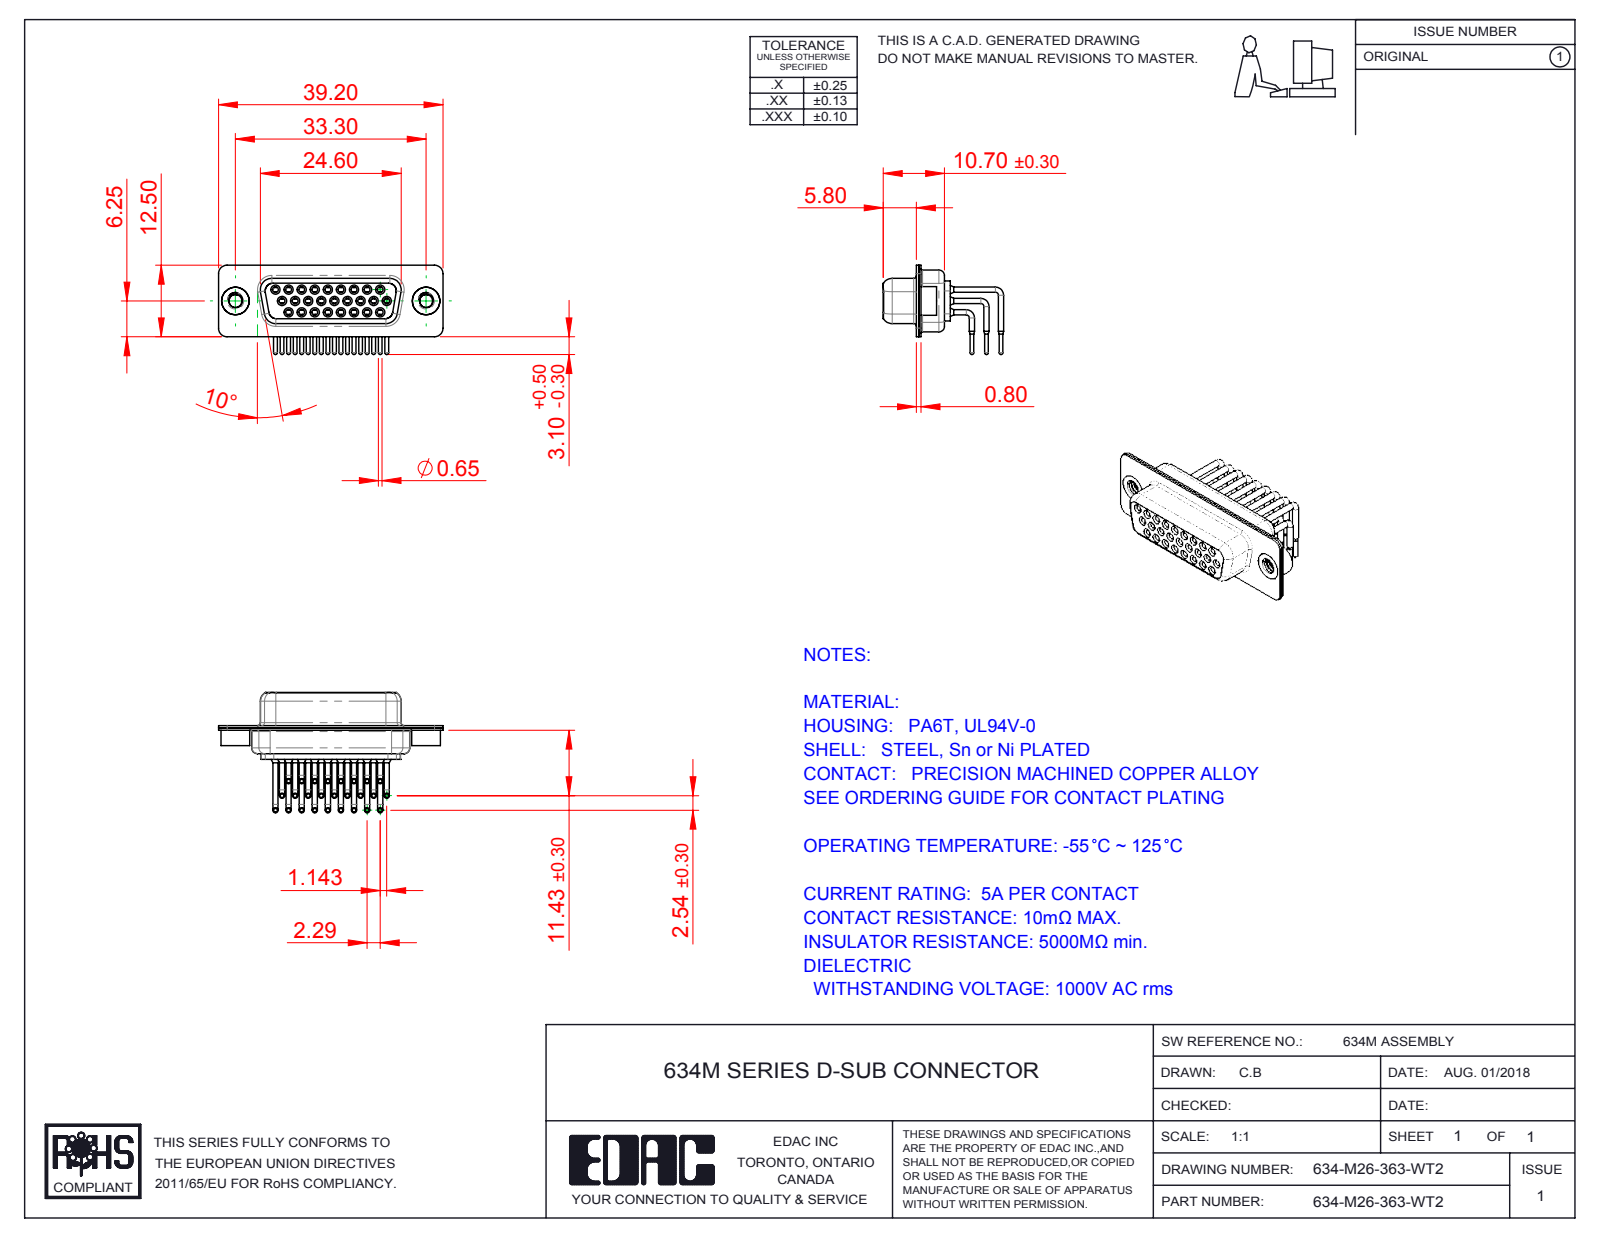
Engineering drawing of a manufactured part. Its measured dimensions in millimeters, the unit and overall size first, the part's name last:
Units: millimetres
Overall size (bounding box): 39.2 × 21.02 × 15.6
Round holes (diameter × count): ⌀1 ×26, ⌀1.1 ×26, ⌀1.7 ×26, ⌀1.8 ×26, ⌀2 ×26, ⌀2.26 ×2, ⌀4 ×2, ⌀4.8 ×2
Round bosses / shafts (diameter × count): ⌀0.9 ×52, ⌀1.6 ×26, ⌀1.5 ×26, ⌀0.65 ×26, ⌀5 ×2, ⌀4.9 ×2, ⌀2 ×1
Partial cylindrical surfaces — rounded edges, fillets, slot ends (radius × count): R1.5 ×16, R2 ×12, R1.35 ×8, R1.6 ×8, R0.25 ×4, R0.5 ×4, R0.6 ×4, R0.65 ×4
Main face-to-face distances: 0.4, 2.3, 1.45, 8.95, 8.5, 1.9, 0.8, 6.2, 0.45, 7.05
Hole centre spacings: 3.96, 2.28, 4.57, 6.05, 2.29, 8.24, 6.86, 6.04
Volume: 2 533 mm³ · Surface area: 8 471 mm²
Bodies: 31 solids, 1657 faces (457 planar, 735 cylindrical, 465 other)
Part name (STEP PRODUCT): 634M Contact Row 2; 634M Shell Front_26 Contacts; 634M Housing_26 Contacts; 634M Shell Rear_26 Contacts (+4 more)
STEP written by: SolidWorks 2016 (CONFIG_CONTROL_DESIGN)
